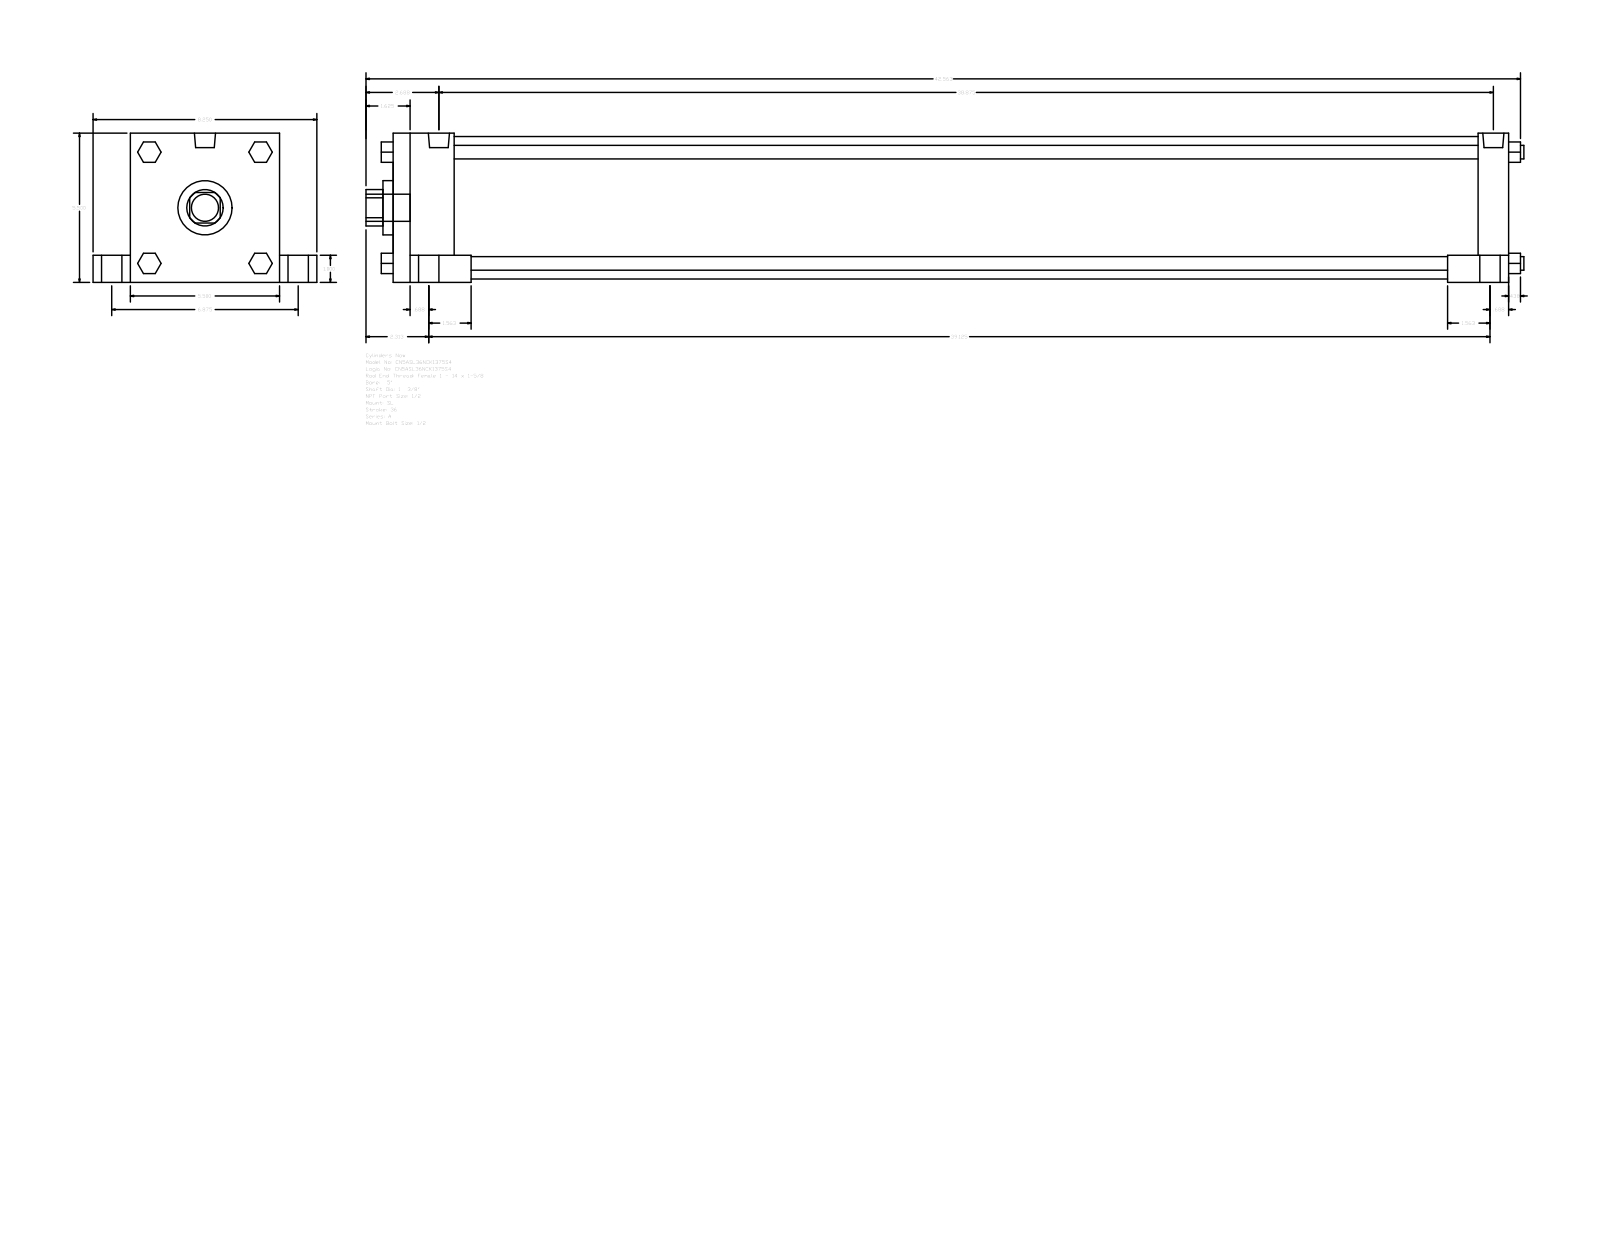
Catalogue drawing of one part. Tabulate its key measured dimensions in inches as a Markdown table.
| quantity | value |
| --- | --- |
| part name | A_SL__0500_1.375 |
| STEP written by | GSSL Pune (CONFIG_CONTROL_DESIGN) |
| units | inches |
| bodies | 0 solids, 150 faces (114 planar, 36 cylindrical, 0 other) |
| overall size | 42.687 × 8.25 × 5.5 |
| round holes (diameter × count) | 1.375 × 1, 2 × 1, 5.25 × 1 |
| round bosses / shafts (diameter × count) | 1 × 5, 0.75 × 4, 0.5 × 4, 0.344 × 4, 0.778 × 2 |
| partial cylindrical surfaces (radius × count) | 0.672 × 1 |
| main face-to-face distances | 5.5, 41.125, 1.125, 2.25, 1, 4.5, 1.375, 6.875, 40, 37.75 |
